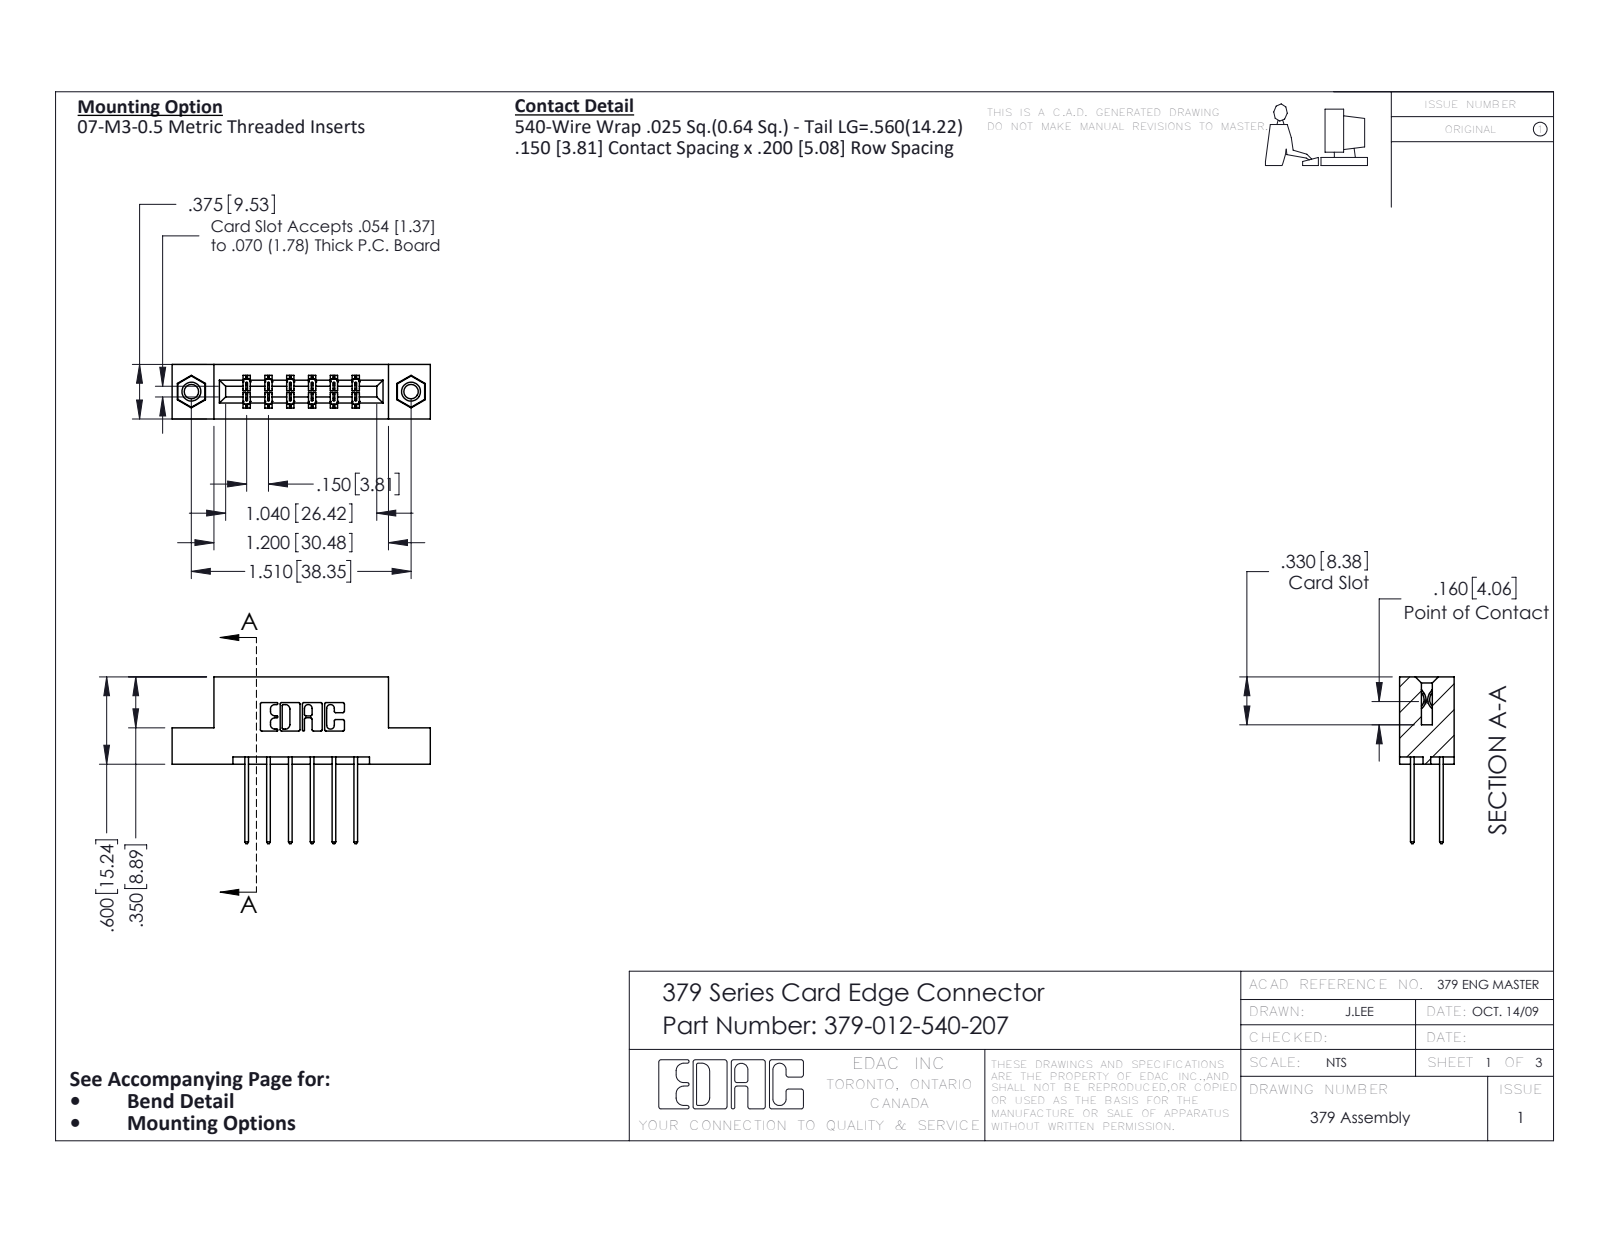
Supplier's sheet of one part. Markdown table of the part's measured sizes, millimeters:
| quantity | value |
| --- | --- |
| part name | 345-292-001_345-293-140; 345-250-001_345-250-005-103; 379-012-540-207; 379 Part_Flush - .156 Dia - TI |
| STEP written by | SolidWorks 2016 (CONFIG_CONTROL_DESIGN) |
| units | millimeters |
| bodies | 15 solids, 798 faces (534 planar, 248 cylindrical, 16 other) |
| overall size | 45.1 × 29.1 × 9.5 |
| volume | 4 380 mm³ |
| surface area | 4 849 mm² |
| round holes (diameter × count) | 2.5 × 2, 3.2 × 2, 4 × 2 |
| round bosses / shafts (diameter × count) | 3.9 × 2 |
| partial cylindrical surfaces (radius × count) | 0.3 × 22, 0.2 × 18, 0.3 × 12, 0.2 × 6, 0.8 × 6, 0.7 × 3, 0.4 × 2, 0.6 × 2 |
| main face-to-face distances | 7.6, 5.1, 3.8, 2.5, 9.5, 1.3, 1.9, 6.4, 8.9, 14 |
| hole center spacings | 38.4 |
